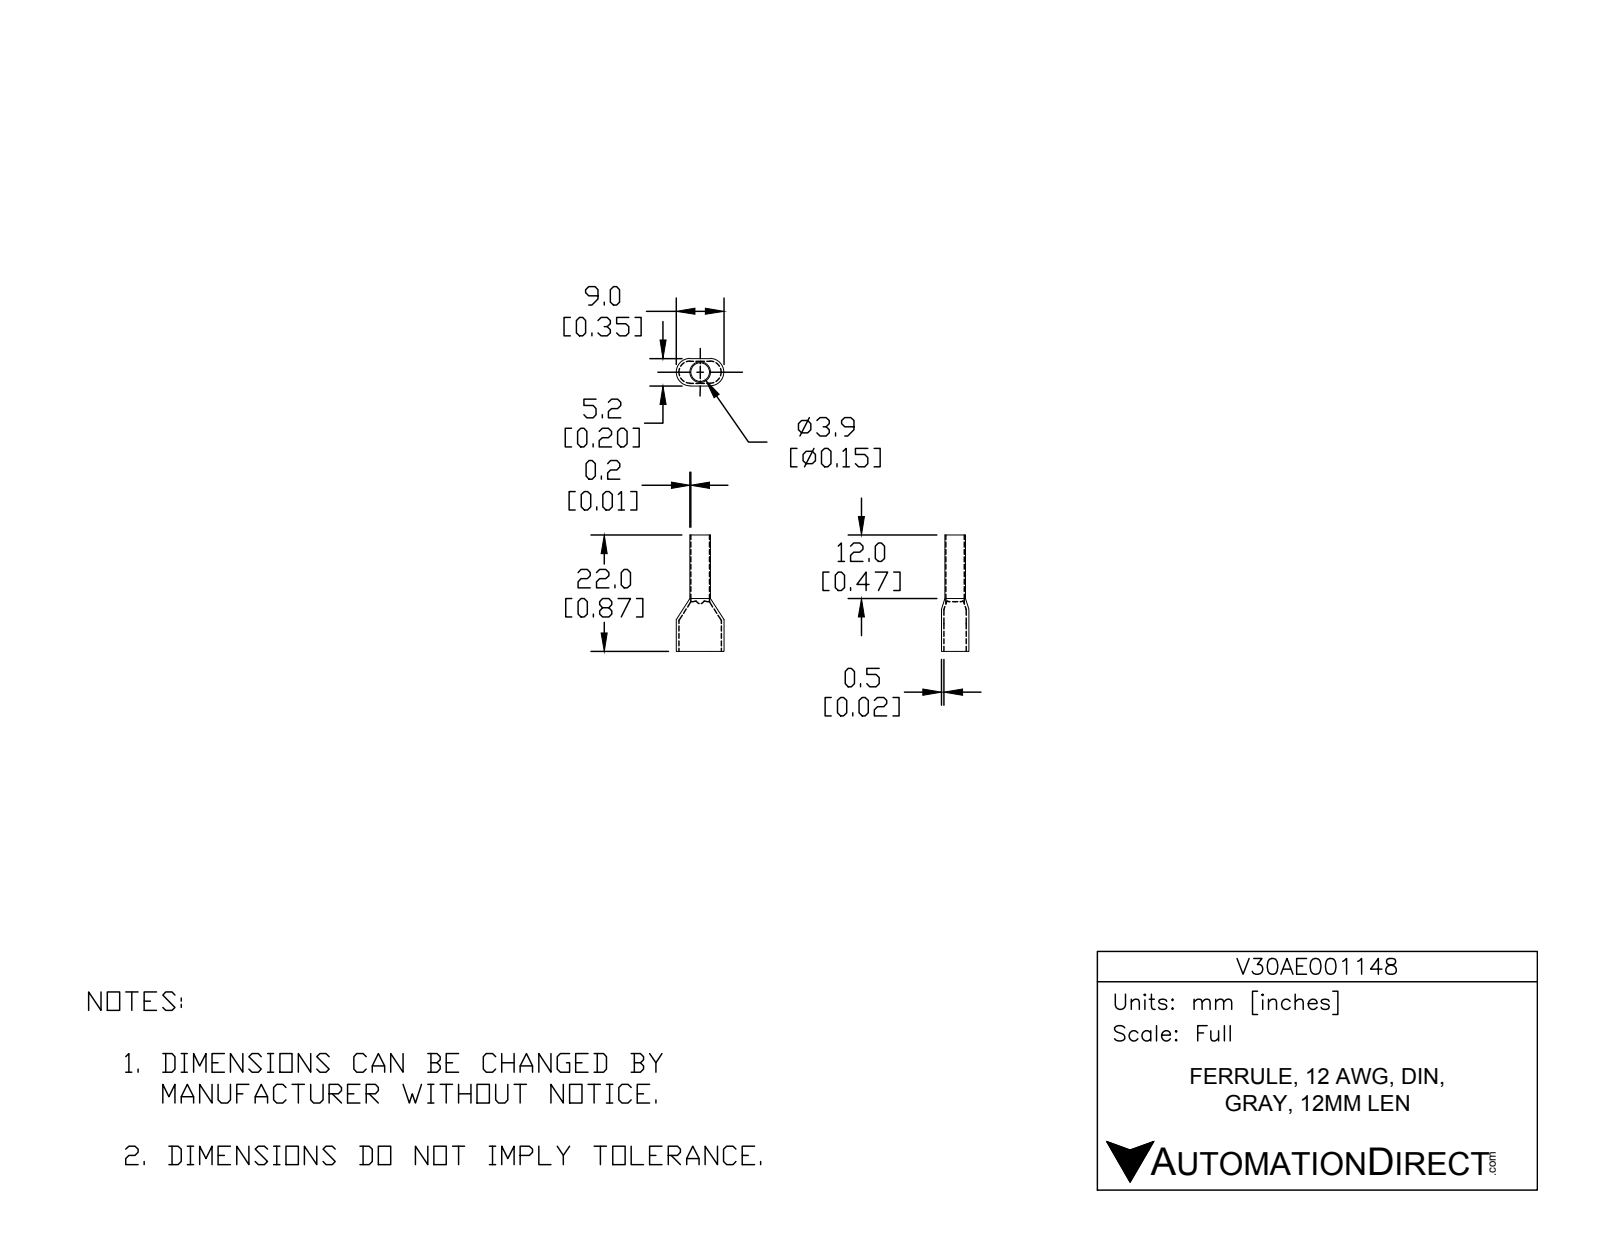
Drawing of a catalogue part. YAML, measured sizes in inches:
part_name: "V30AE001148"
step_written_by: "SolidWorks 2017 (AUTOMOTIVE_DESIGN)"
units: inches
bodies: {solids: 2, faces: 38, planar: 16, cylindrical: 22, other: 0}
overall_size: [0.866, 0.354, 0.205]
volume: 0.008
surface_area: 1.1
round_holes:
  - {diameter: 0.138, count: 1}
round_bosses_or_shafts:
  - {diameter: 0.154, count: 1}
partial_cylinders:
  - {radius: 0.083, count: 6}
  - {radius: 0.102, count: 6}
face_to_face_distances: [0.02, 0.185, 0.205, 0.165, 0.394, 0.866, 0.472, 0.374, 0.492]
